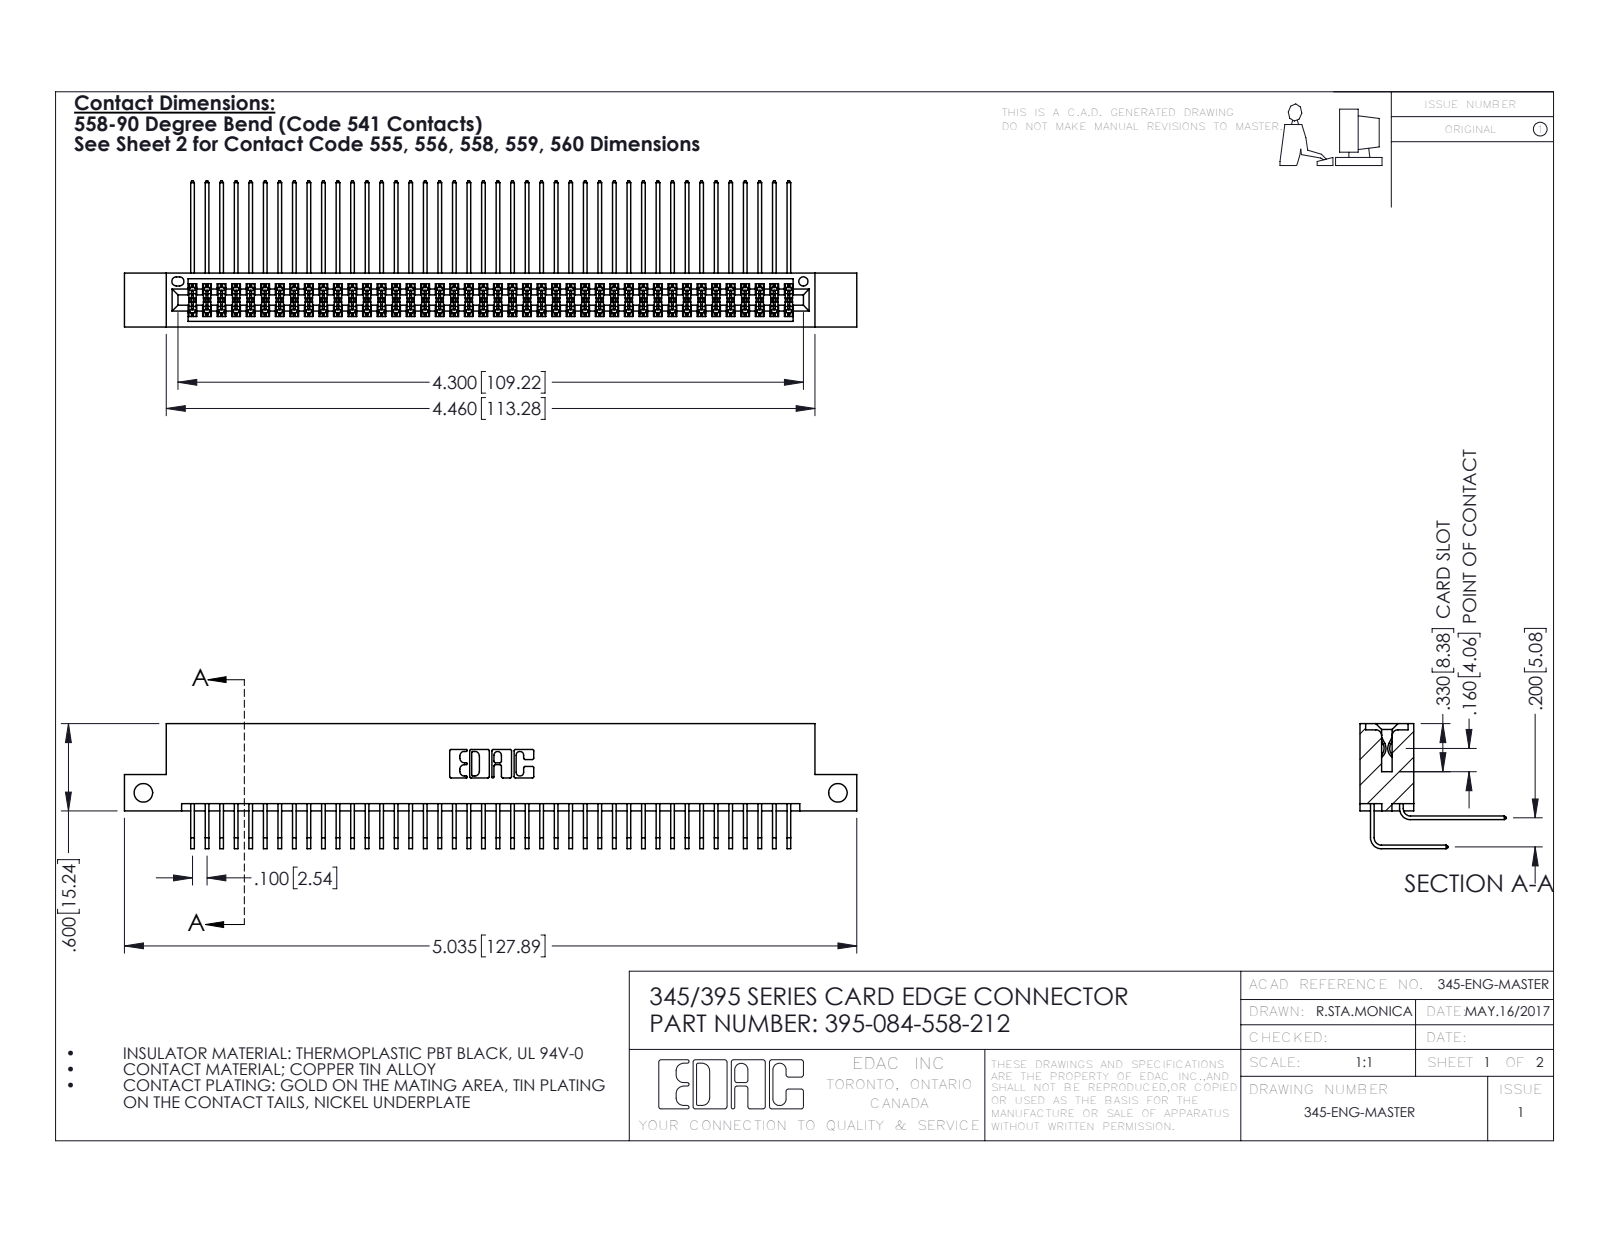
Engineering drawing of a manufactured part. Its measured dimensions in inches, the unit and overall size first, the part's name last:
Units: inches
Overall size (bounding box): 5.035 × 1.005 × 0.859
Round holes (diameter × count): ⌀0.128 ×2, ⌀0.064 ×1
Partial cylindrical surfaces — rounded edges, fillets, slot ends (radius × count): R0.006 ×127, R0.01 ×22, R0.007 ×6, R0.031 ×6, R0.026 ×3, R0.014 ×2, R0.019 ×2, R0.022 ×2
Main face-to-face distances: 0.072, 0.298, 0.2, 0.37, 0.098, 0.272, 0.025, 0.225, 0.025, 0.175
Hole centre spacings: 4.775
Volume: 0.782 in³ · Surface area: 32.7 in²
Bodies: 85 solids, 4494 faces (3020 planar, 1474 cylindrical, 0 other)
Part name (STEP PRODUCT): 345-292-001_558 559 Tail - 1; 345-292-001_558 Tail - 2; 345 Part_Flush Mounting Lugs - Side Mount; 395-084-558-212
STEP written by: SolidWorks 2016 (CONFIG_CONTROL_DESIGN)
